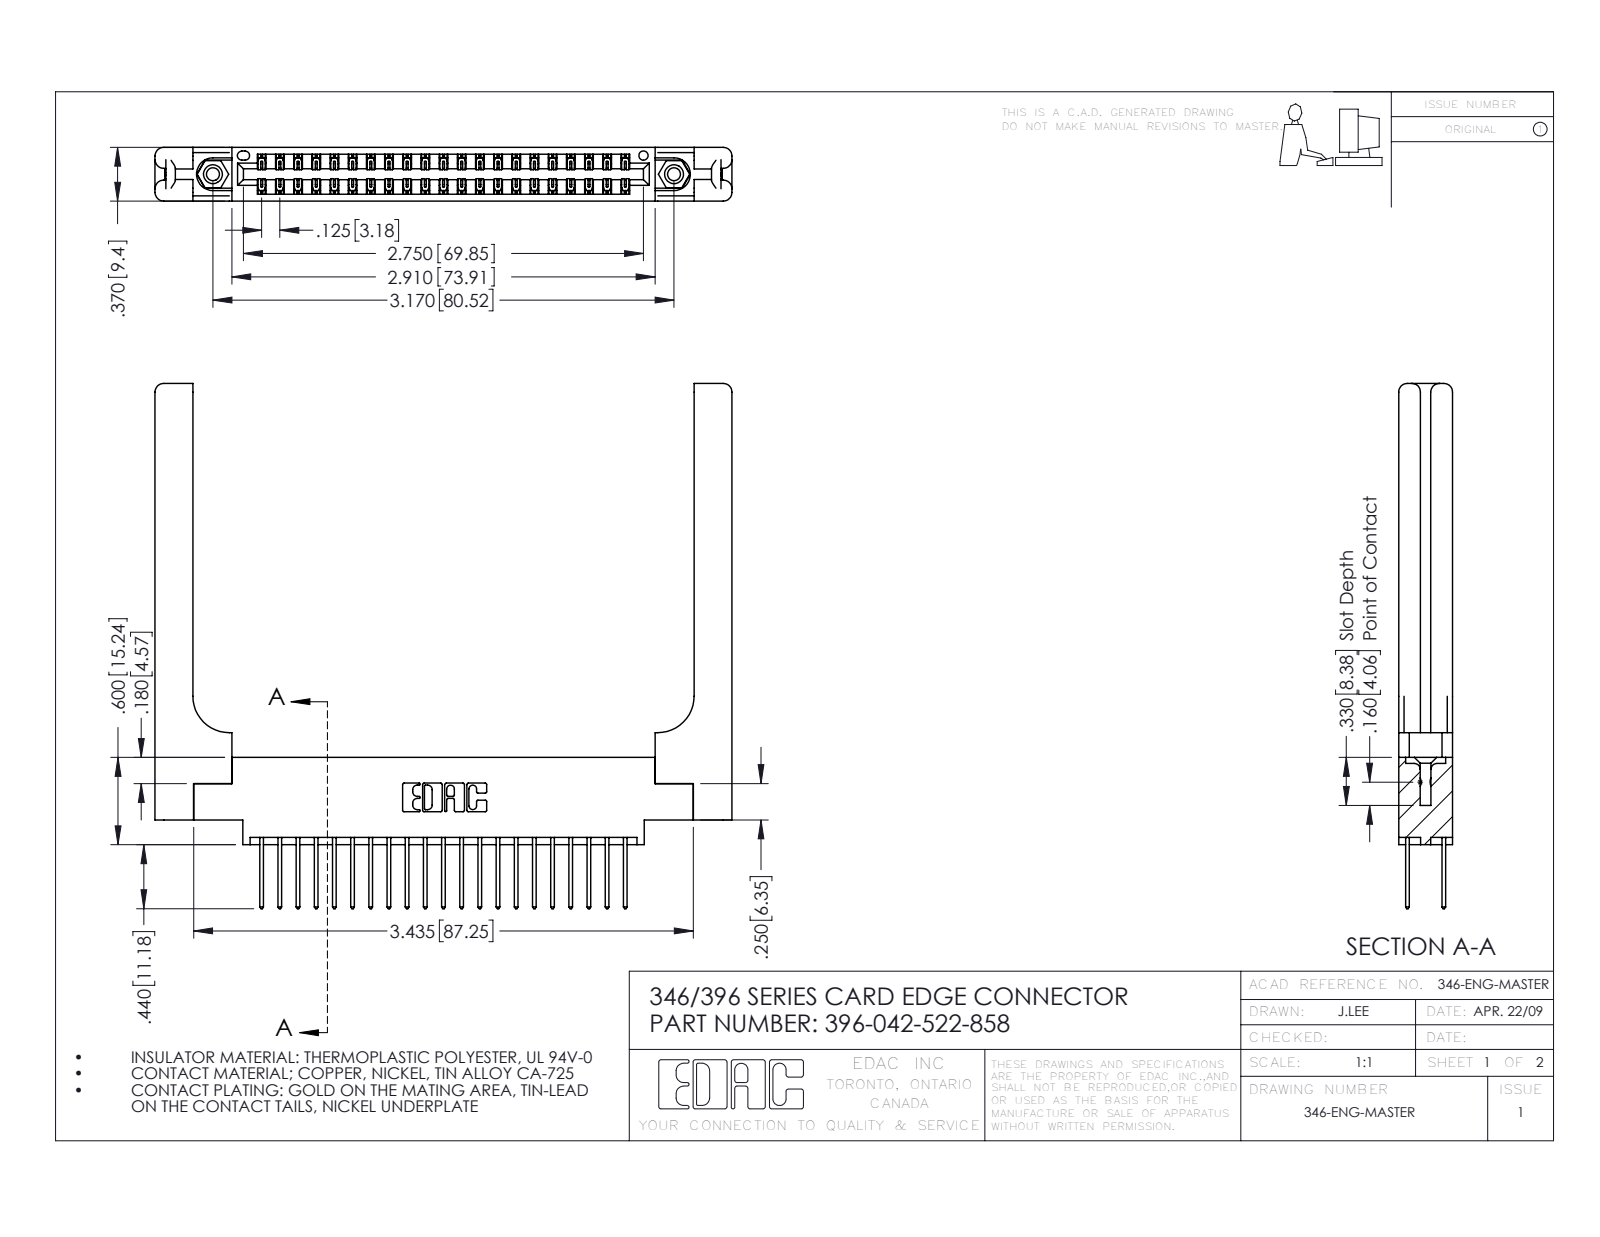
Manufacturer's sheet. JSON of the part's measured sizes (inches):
{"part_name": "345-250-001_345-250-001-102; 345-292-001_345-293-122; 396-042-522-858; 346-220-058_345-220-058 (+1 more)", "step_written_by": "SolidWorks 2016 (CONFIG_CONTROL_DESIGN)", "units": "inches", "bodies": {"solids": 47, "faces": 2566, "planar": 1698, "cylindrical": 808, "other": 60}, "overall_size": [3.966, 3.61, 0.37], "volume_in3": 1.044, "surface_area_in2": 28.73, "round_holes": [[0.089, 2], [0.125, 2], [0.156, 2], [0.064, 1]], "round_bosses_or_shafts": [[0.155, 2]], "partial_cylinders_radius": [[0.006, 63], [0.01, 42], [0.01, 22], [0.06, 16], [0.007, 6], [0.031, 6], [0.026, 3], [0.014, 2]], "face_to_face_distances": [0.37, 0.072, 0.048, 0.322, 0.148, 0.15, 0.25, 0.025, 0.298, 0.275], "hole_center_spacings": [0.246, 2.963, 3.17]}
